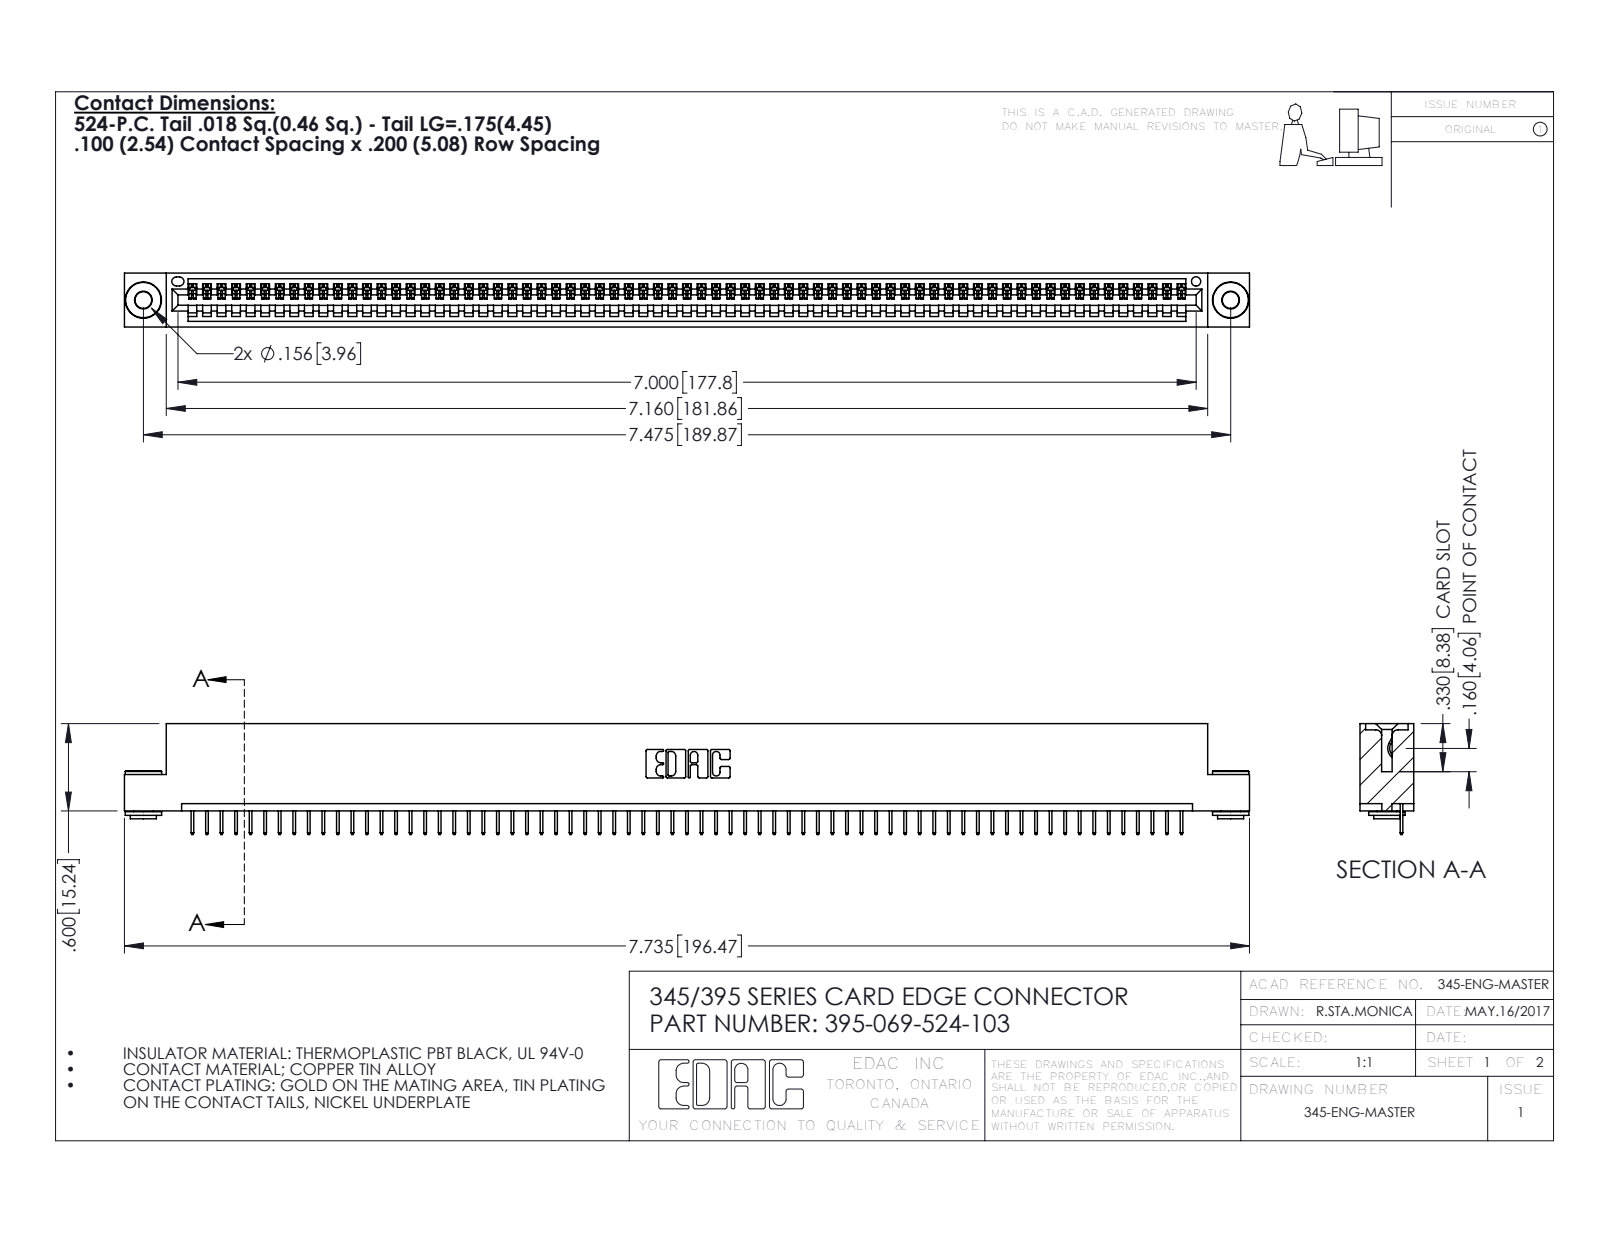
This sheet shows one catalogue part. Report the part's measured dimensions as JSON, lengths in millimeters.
{"part_name": "345-250-002_345-250-002-102; 395-069-524-103; 345 Part_Flush Mounting Lugs - 0.156 Dia-TH; 345-292-001_345-293-124", "step_written_by": "SolidWorks 2016 (CONFIG_CONTROL_DESIGN)", "units": "millimeters", "bodies": {"solids": 72, "faces": 4442, "planar": 3264, "cylindrical": 1170, "other": 8}, "overall_size": [196.5, 19.4, 9.4], "volume_mm3": 18630, "surface_area_mm2": 24460, "round_holes": [[2.9, 2], [4, 2], [1.6, 1]], "round_bosses_or_shafts": [[6.4, 2], [4.6, 2], [3.5, 2]], "partial_cylinders_radius": [[0.2, 138], [0.3, 22], [0.2, 6], [0.8, 6], [0.7, 3], [0.8, 2], [1, 2], [0.4, 1]], "face_to_face_distances": [1.8, 7.6, 9.4, 5.1, 0.6, 2.5, 6.9, 5.7, 1.8, 3.8], "hole_center_spacings": [6.9, 183.9, 189.9]}
